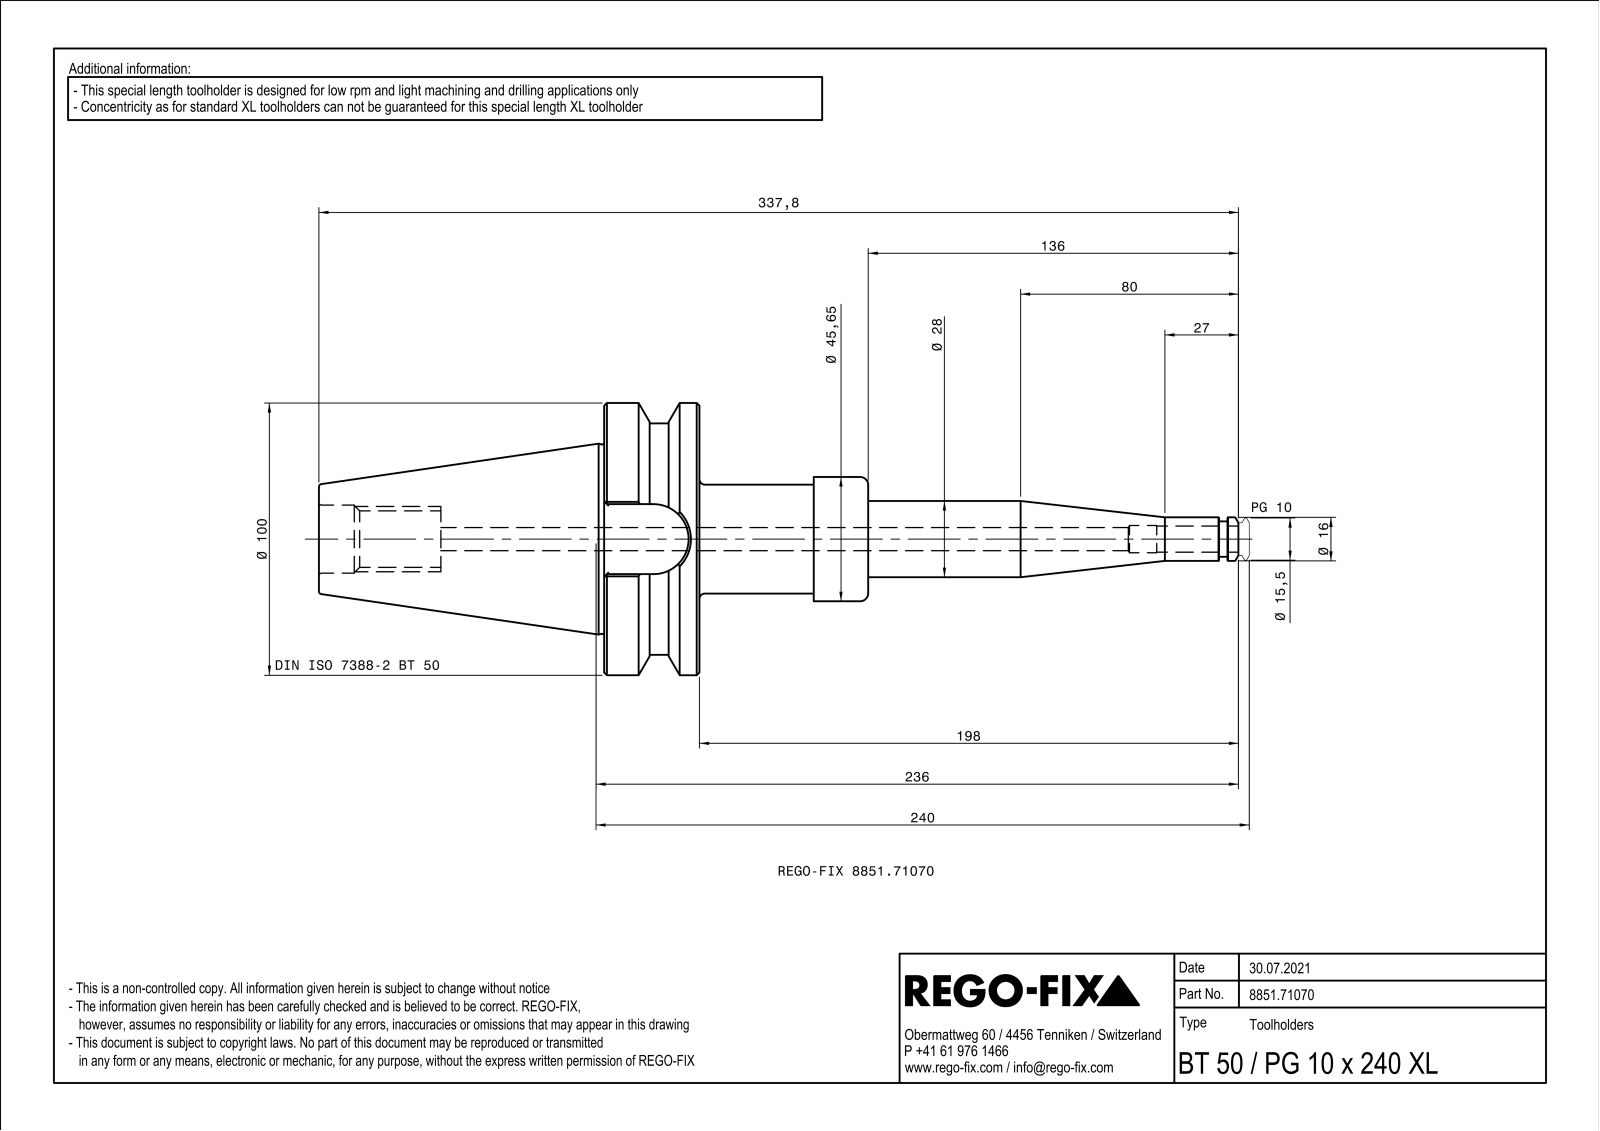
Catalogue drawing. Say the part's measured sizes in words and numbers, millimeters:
The part is named "NOCUT". Its 3-D file was written by "SIEMENS PLM Software Solid Edge ST10 (AUTOMOTIVE_DESIGN)". It is 1 solid with 137 faces: 44 planar, 33 cylindrical and 60 other. Overall it measures 337.8 by 100 by 100 millimeters. Its volume is 568 507 cubic millimeters and its surface area 84 679 square millimeters. Round holes: 1 of diameter 9, 1 of diameter 10, 1 of diameter 20.75, 1 of diameter 25, 1 of diameter 29, 1 of diameter 38.38, 1 of diameter 40.05, 1 of diameter 43.3. Round bosses or shafts: 1 of diameter 100, 1 of diameter 85, 1 of diameter 45.65, 1 of diameter 40, 1 of diameter 34, 1 of diameter 33, 1 of diameter 28, 1 of diameter 24.7. Partial cylindrical surfaces (rounded edges, fillets, slot ends): 4 of radius 0.5, 1 of radius 12.85, 1 of radius 22.77. The main face-to-face distances are 35, 70.7, 139.8, 104.8, 38.5, 62, 97, 201.8, 6, 14.
